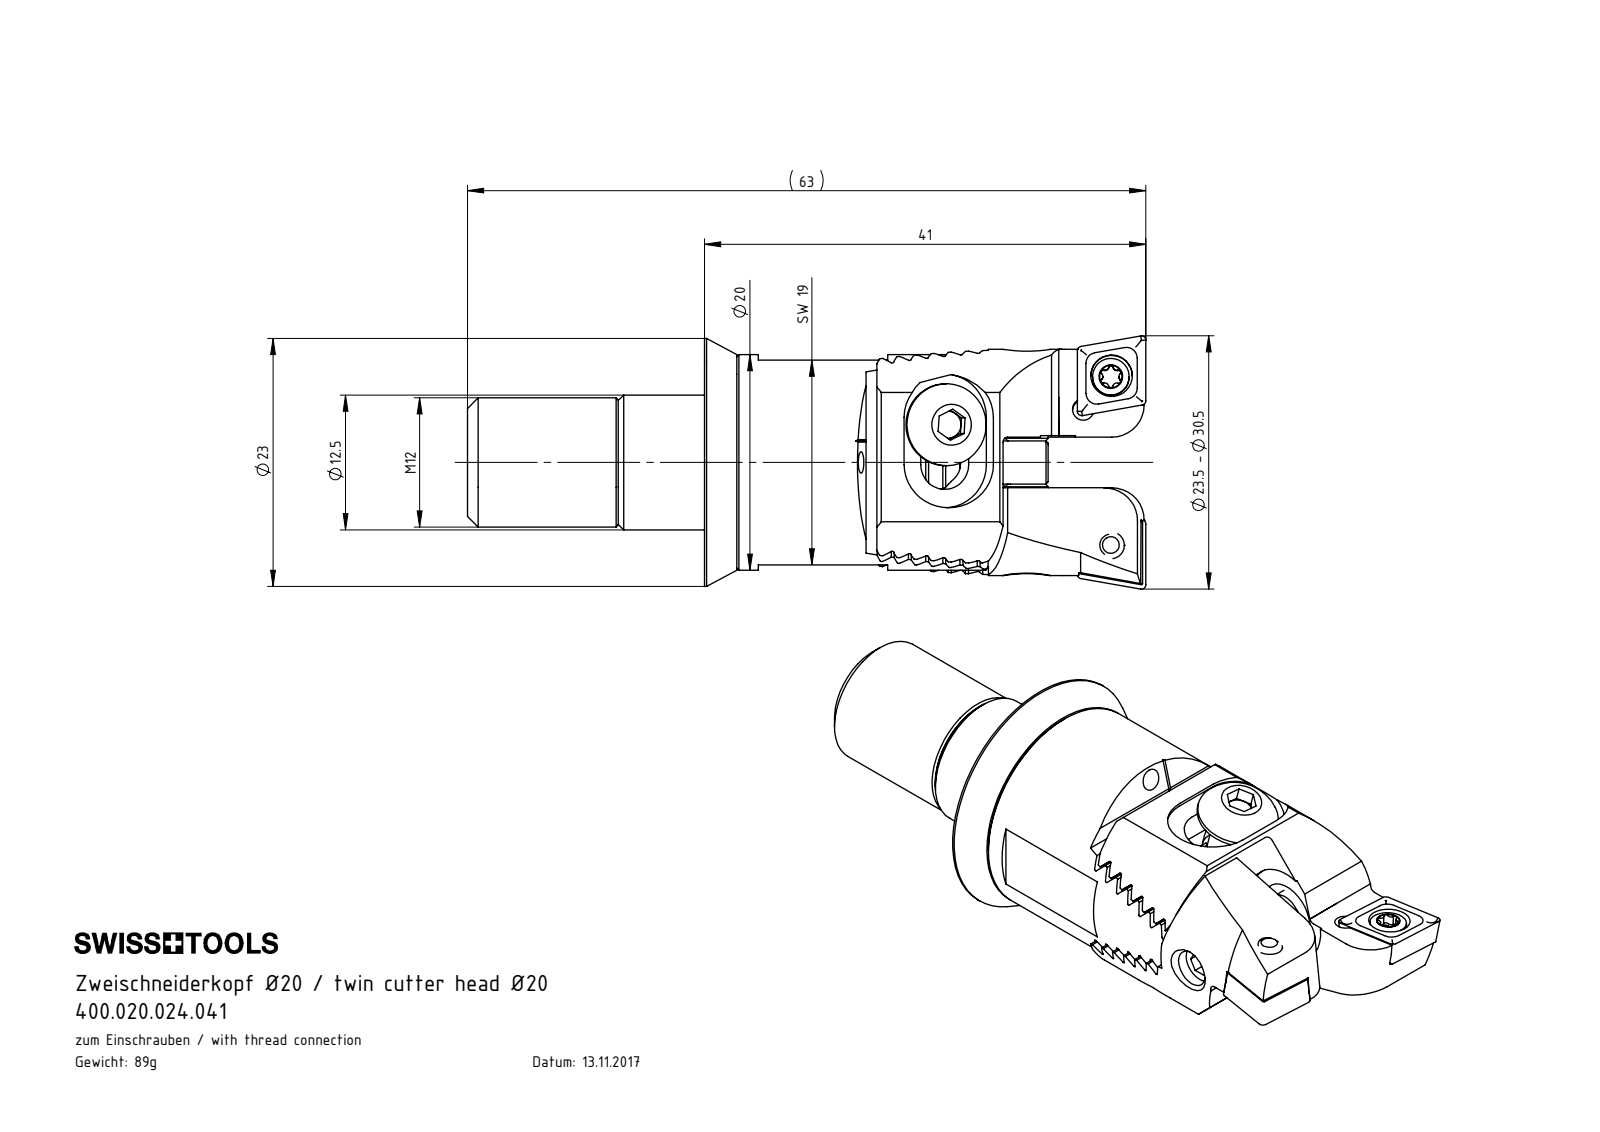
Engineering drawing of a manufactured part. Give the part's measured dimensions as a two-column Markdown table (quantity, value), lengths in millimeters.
| quantity | value |
| --- | --- |
| part name | Z20-WCA.001.015; Z20-ER3.001.007_A; CCMT060204; Z20-ER1.002.008_A_PreviewCfg (+7 more) |
| STEP written by | SolidWorks 2017 (CONFIG_CONTROL_DESIGN) |
| units | millimeters |
| bodies | 14 solids, 764 faces (340 planar, 227 cylindrical, 197 other) |
| overall size | 62.96 × 23.5 × 23 |
| volume | 11 454 mm³ |
| surface area | 9 433 mm² |
| round holes (diameter × count) | 2 × 6, 3.3 × 3, 1 × 2, 2.05 × 2, 2.8 × 2, 3.85 × 2, 5 × 2, 2.5 × 1, 3.5 × 1, 6.8 × 1, 8.5 × 1, 9.1 × 1 |
| round bosses / shafts (diameter × count) | 4 × 4, 7.6 × 2, 3.4 × 2, 2.5 × 2, 23 × 1, 20 × 1, 12 × 1, 8 × 1 |
| partial cylindrical surfaces (radius × count) | 0.12 × 26, 0.21 × 12, 0.36 × 10, 1 × 8, 0.5 × 4, 2.3 × 4, 4 × 4, 0.36 × 2 |
| main face-to-face distances | 1.43, 2.86, 3, 5.71, 4.29, 4.28, 7.14, 2.85, 2.57, 7.15 |
| hole center spacings | 3.99, 4.09, 6, 13.08, 13.17, 15.96, 9.77, 11.6 |
